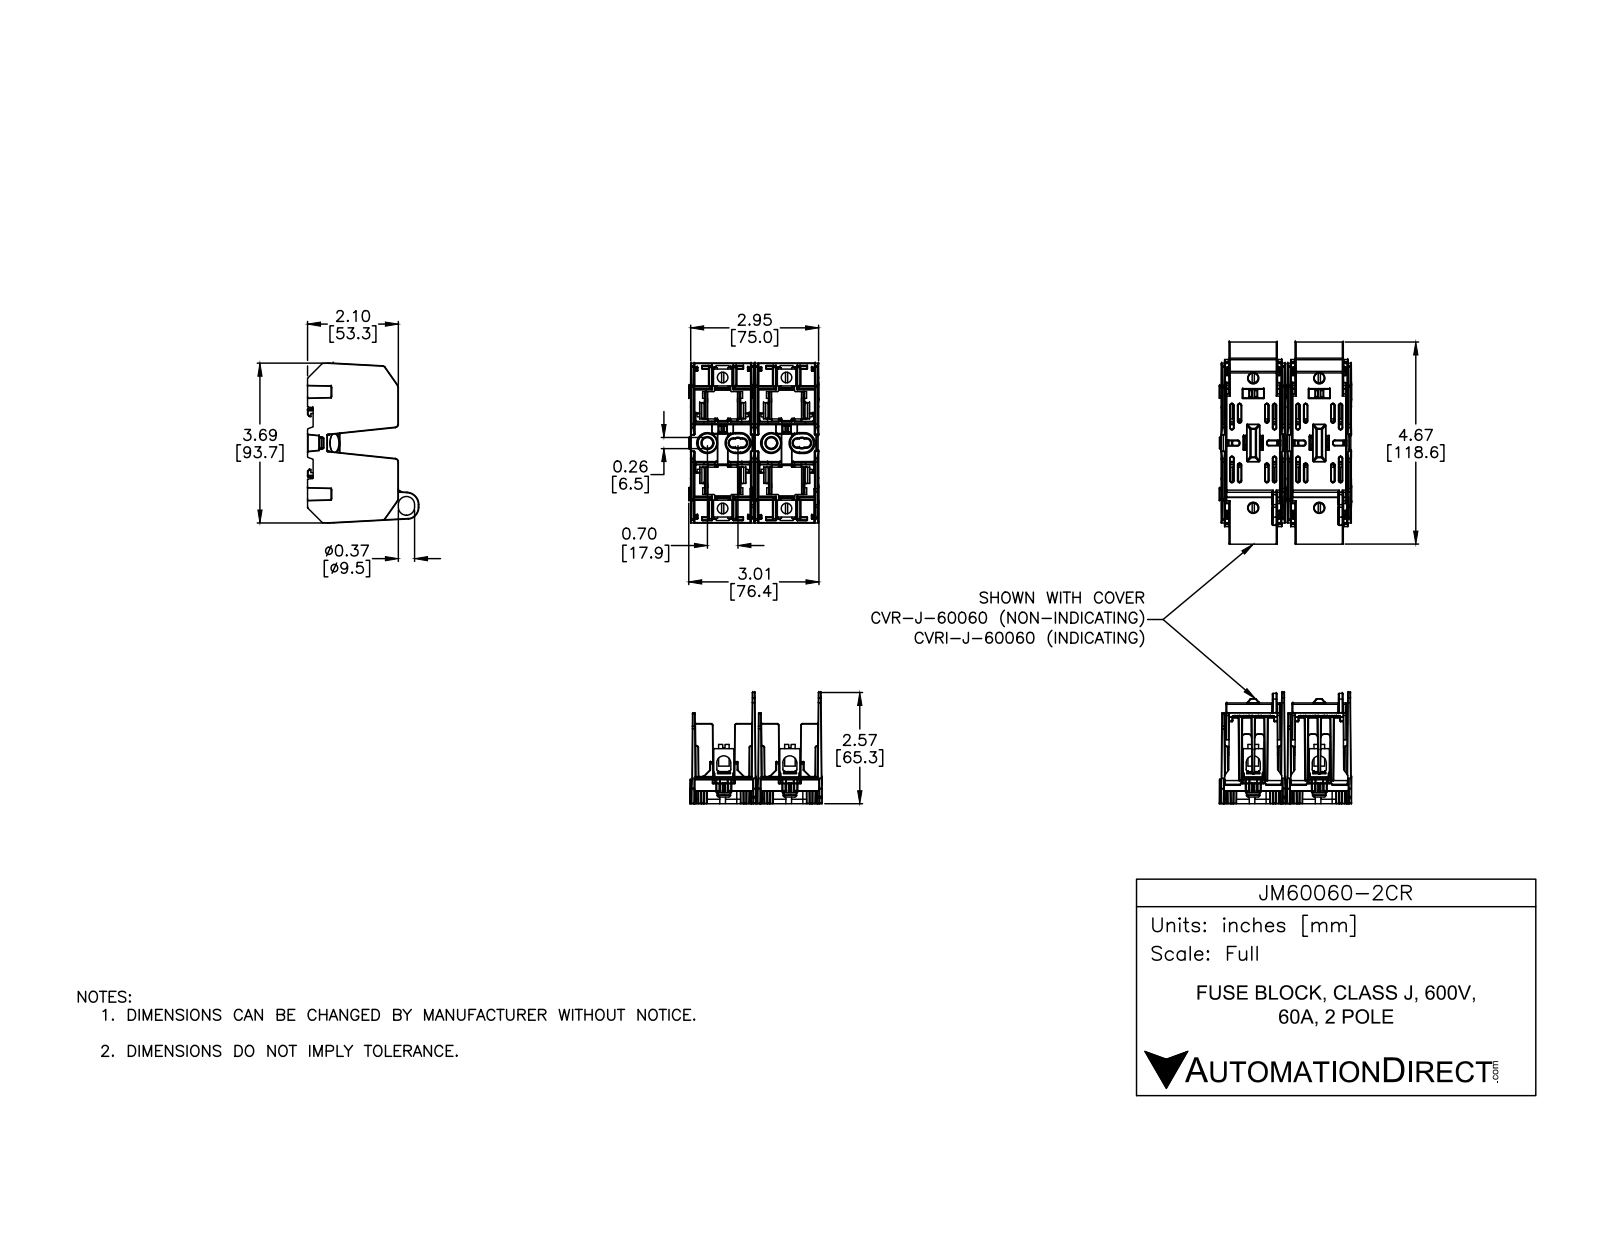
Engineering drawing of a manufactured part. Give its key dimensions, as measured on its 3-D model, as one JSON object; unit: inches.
{"part_name": "JM60060-1CR; JM60060-2CR", "step_written_by": "SolidWorks 2016 (AUTOMOTIVE_DESIGN)", "units": "inches", "bodies": {"solids": 16, "faces": 768, "planar": 420, "cylindrical": 348, "other": 0}, "overall_size": [3.577, 2.546, 1.158], "volume_in3": 0.709, "surface_area_in2": 36.6, "round_holes": [[0.225, 4], [0.244, 4]], "round_bosses_or_shafts": [[0.05, 16], [0.244, 4]], "partial_cylinders_radius": [[0.012, 36], [0.039, 32], [0.02, 16], [0.079, 16], [0.031, 8], [0.05, 8], [0.051, 8], [0.063, 8]], "face_to_face_distances": [0.032, 0.028, 1.48, 0.06, 1.448, 0.028, 1.483, 0.073, 0.041, 0.013], "hole_center_spacings": [1.483, 0.676, 0.676, 1.628, 1.676, 2.351, 2.352, 3.027]}
